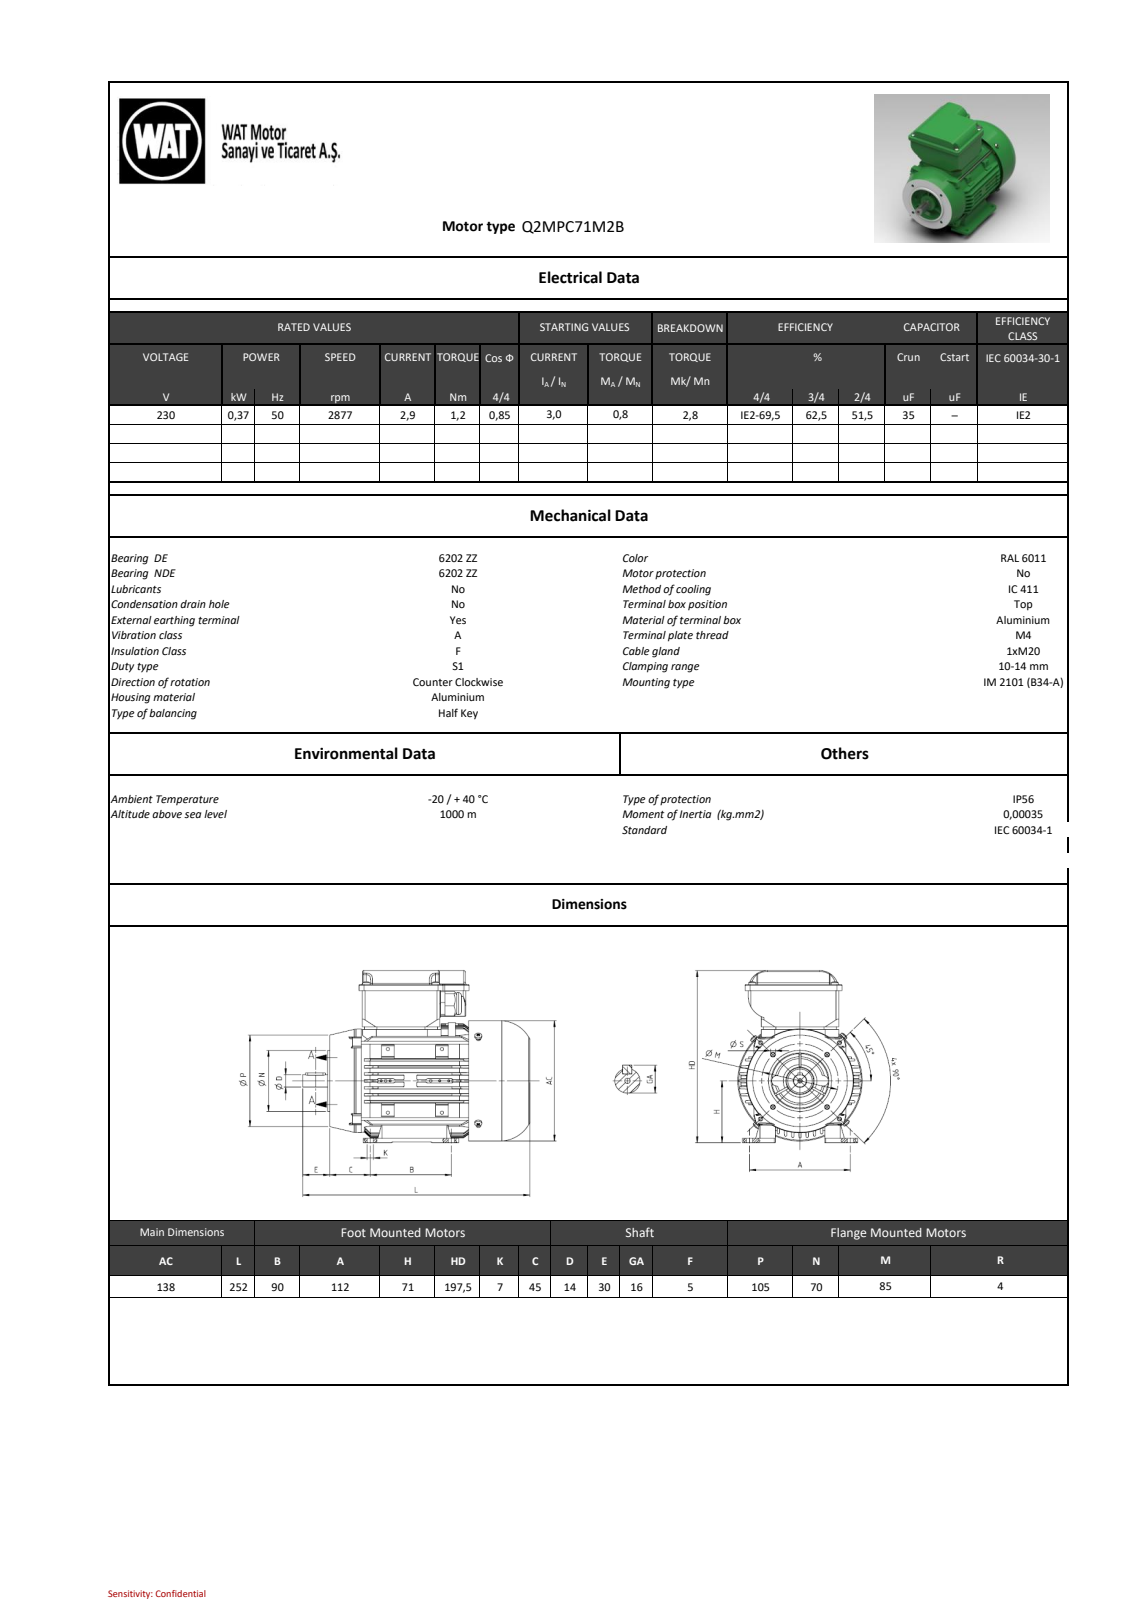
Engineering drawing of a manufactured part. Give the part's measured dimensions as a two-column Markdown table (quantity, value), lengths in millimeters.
| quantity | value |
| --- | --- |
| part name | BY6434017xx_004-TK_QM63-80; BY6424130xx_004-TKK_QM63-80; BY6432003xx_006-MOTOR_KAPAGI_QS71_FC_ISLEME; 641304741_AZ-KAMA PARALEL A 5x5x22 St50 DIN6885 (+8 more) |
| STEP written by | SIEMENS PLM Software NX2206.8101 (AUTOMOTIVE_DESIGN) |
| units | millimeters |
| bodies | 26 solids, 2792 faces (1338 planar, 781 cylindrical, 673 other) |
| overall size | 252 × 197.5 × 138 |
| volume | 767 801 mm³ |
| surface area | 490 639 mm² |
| round holes (diameter × count) | 3.3 × 9, 3.65 × 8, 4.5 × 8, 3 × 7, 2.5 × 6, 4.65 × 4, 4.8 × 4, 5.2 × 4, 7 × 4, 3.7 × 3, 4.6 × 2, 5 × 1 |
| round bosses / shafts (diameter × count) | 8 × 8, 4 × 8, 3 × 8, 12 × 4, 3.3 × 4, 138 × 1, 136 × 1, 70 × 1 |
| partial cylindrical surfaces (radius × count) | 1 × 151, 2 × 57, 0.5 × 41, 1.2 × 36, 3.25 × 16, 2.5 × 14, 5.5 × 13, 0.3 × 12 |
| main face-to-face distances | 3, 4, 1, 189.5, 5, 67.5, 19, 182.5, 185.5, 154.5 |
| hole center spacings | 55, 36.59, 60, 28.5, 37.26, 61.87, 66.91, 68.11 |
